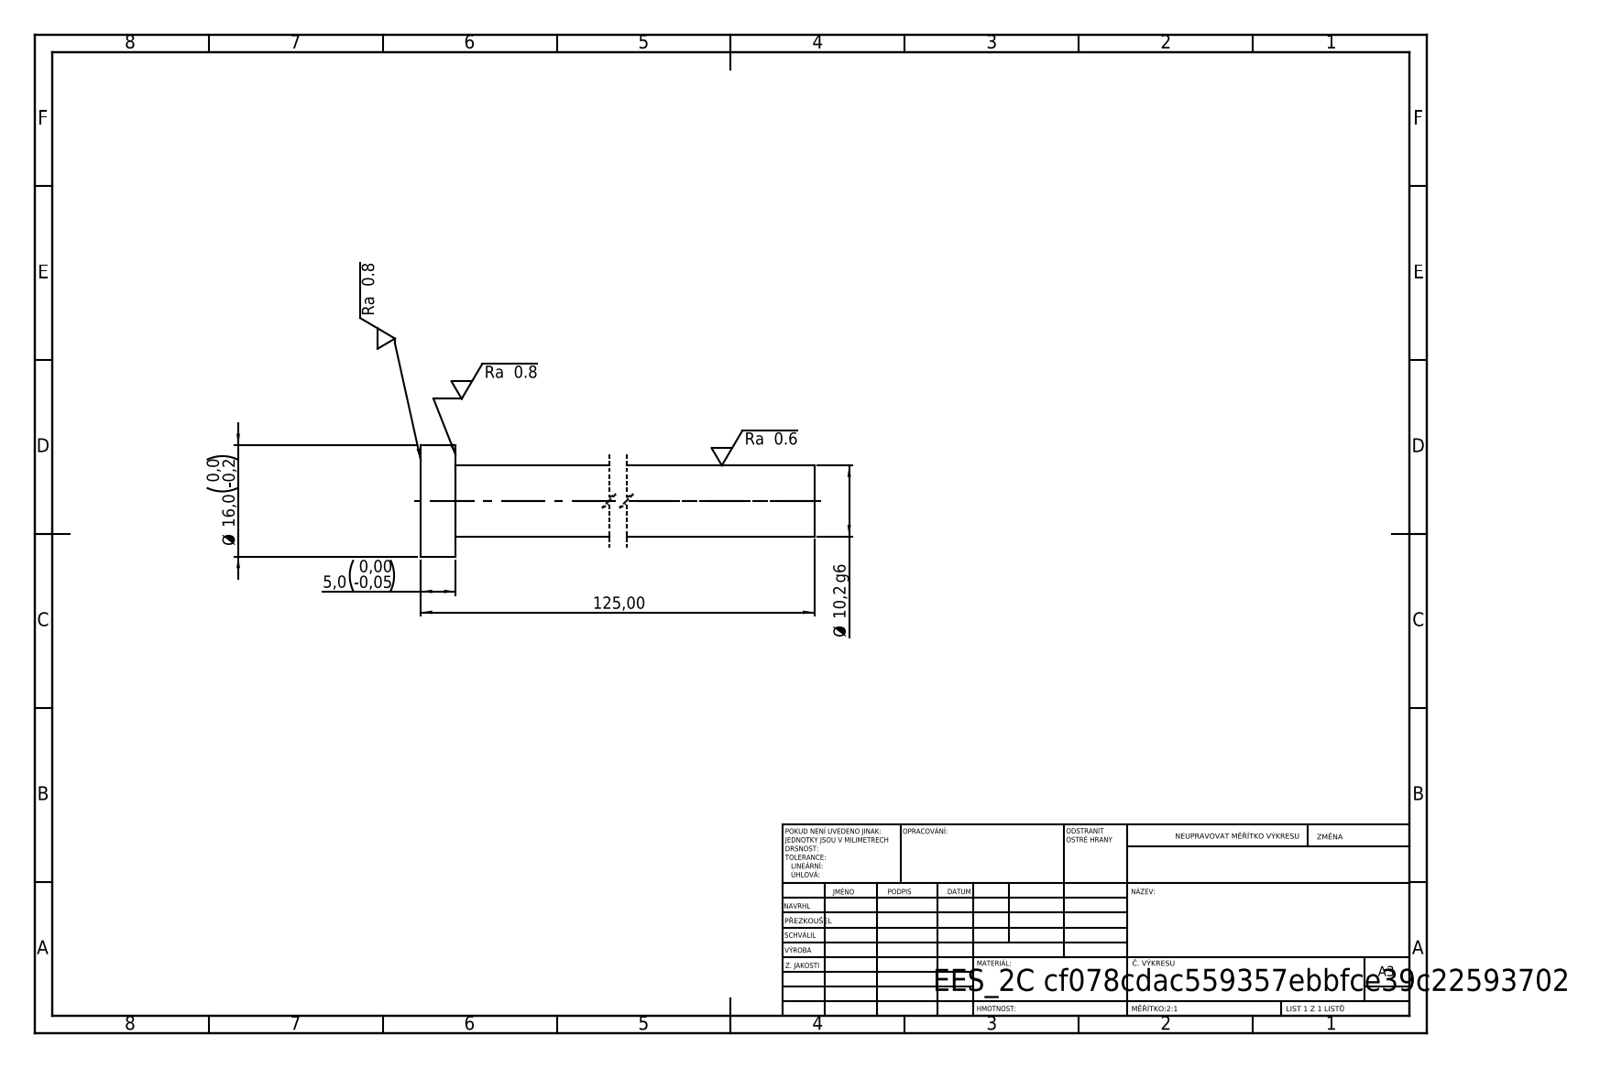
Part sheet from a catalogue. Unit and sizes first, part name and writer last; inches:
Units: inches
Overall size (bounding box): 4.921 × 0.63 × 0.63
Round bosses / shafts (diameter × count): ⌀0.63 ×1, ⌀0.402 ×1
Main face-to-face distances: 0.197, 4.921, 4.724
Volume: 0.66 in³ · Surface area: 6.973 in²
Bodies: 1 solid, 7 faces (3 planar, 4 cylindrical, 0 other)
STEP written by: SolidWorks 2019 (CONFIG_CONTROL_DESIGN)
